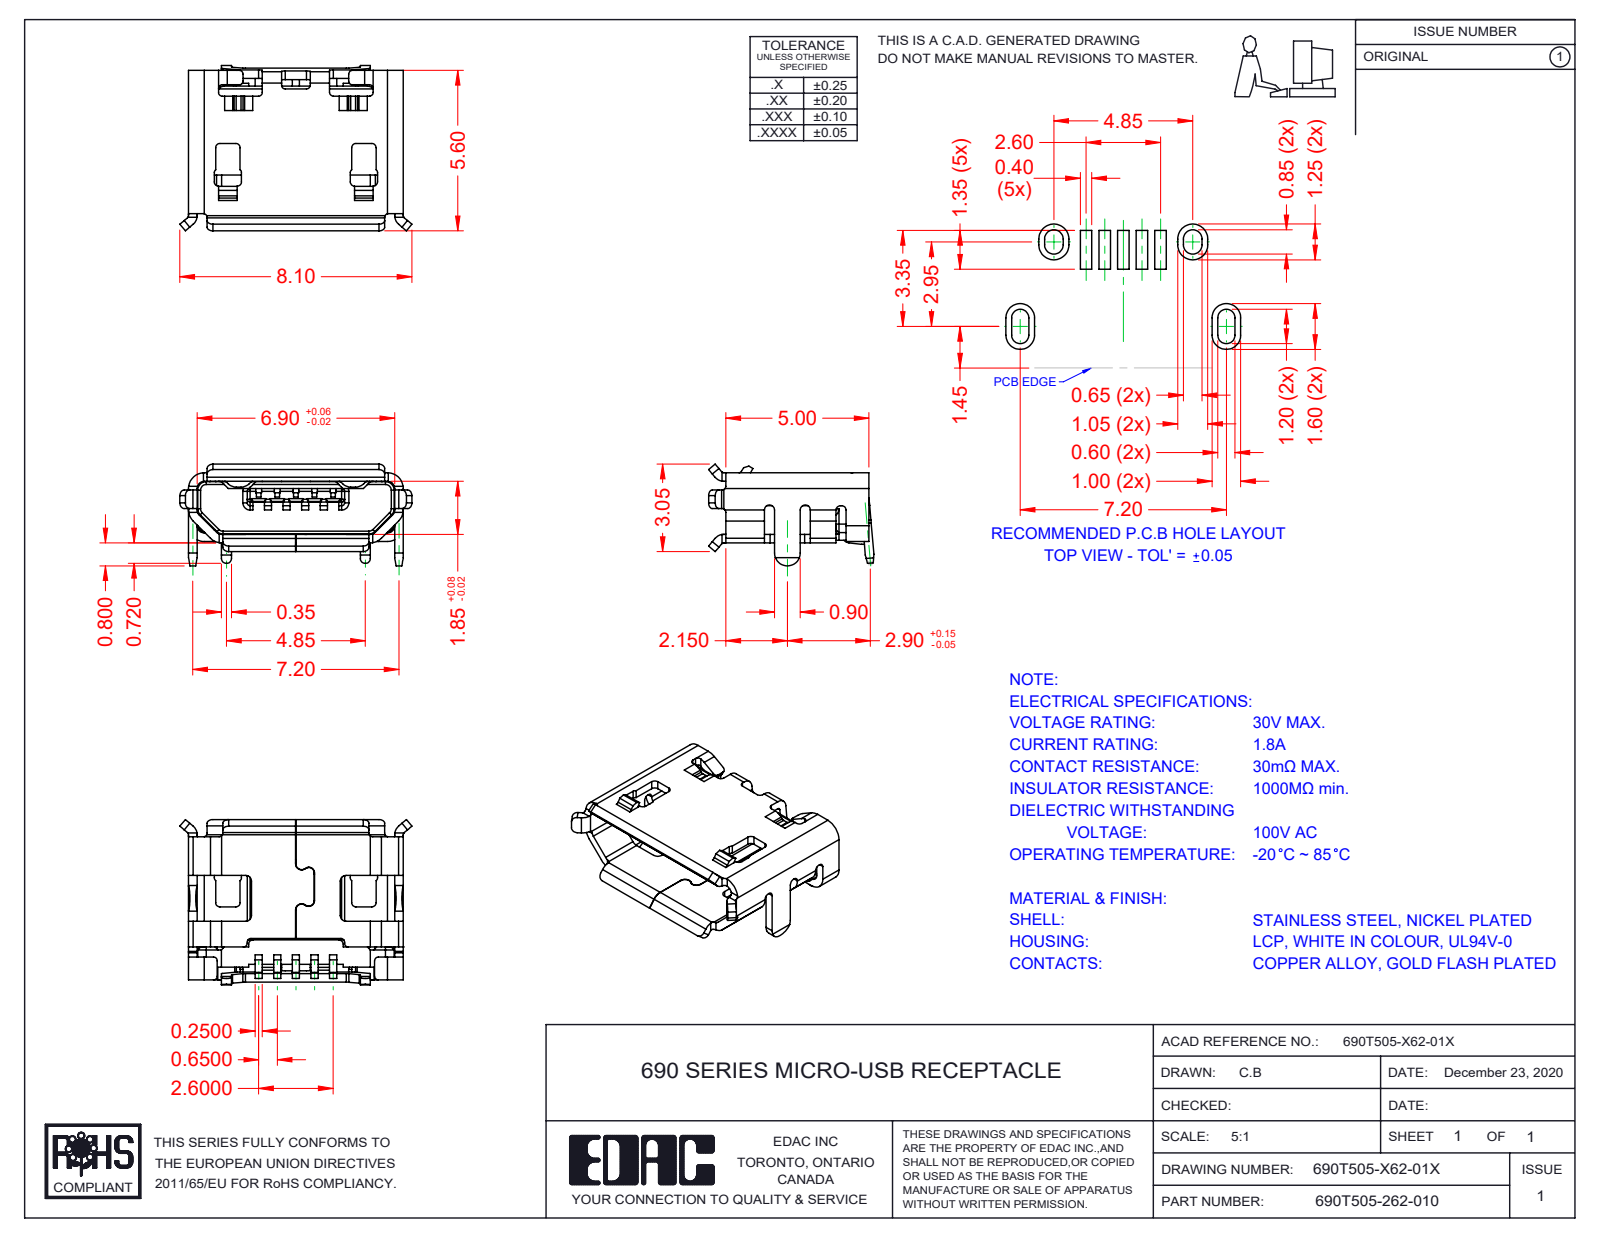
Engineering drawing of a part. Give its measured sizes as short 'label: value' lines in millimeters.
name: SHELL 690T505-X62-01X; Insulator 690T505-X62-01X_WHITE; 690T505-162-010
written by: SolidWorks 2020 (AUTOMOTIVE_DESIGN)
unit: mm
bodies: 2 solids, 653 faces (415 planar, 199 cylindrical, 39 other)
size: 8.1 × 5.77 × 3.55
volume: 43 mm³; area: 279 mm²
rounds: 42× R0.13, 26× R0.1, 20× R0.15, 16× R0.2, 13× R0.4, 11× R0.3, 10× R0.25, 9× R0.55
face distances: 2.15, 1.85, 2.45, 0.95, 7.2, 1.5, 0.55, 0.9, 0.35, 0.6
